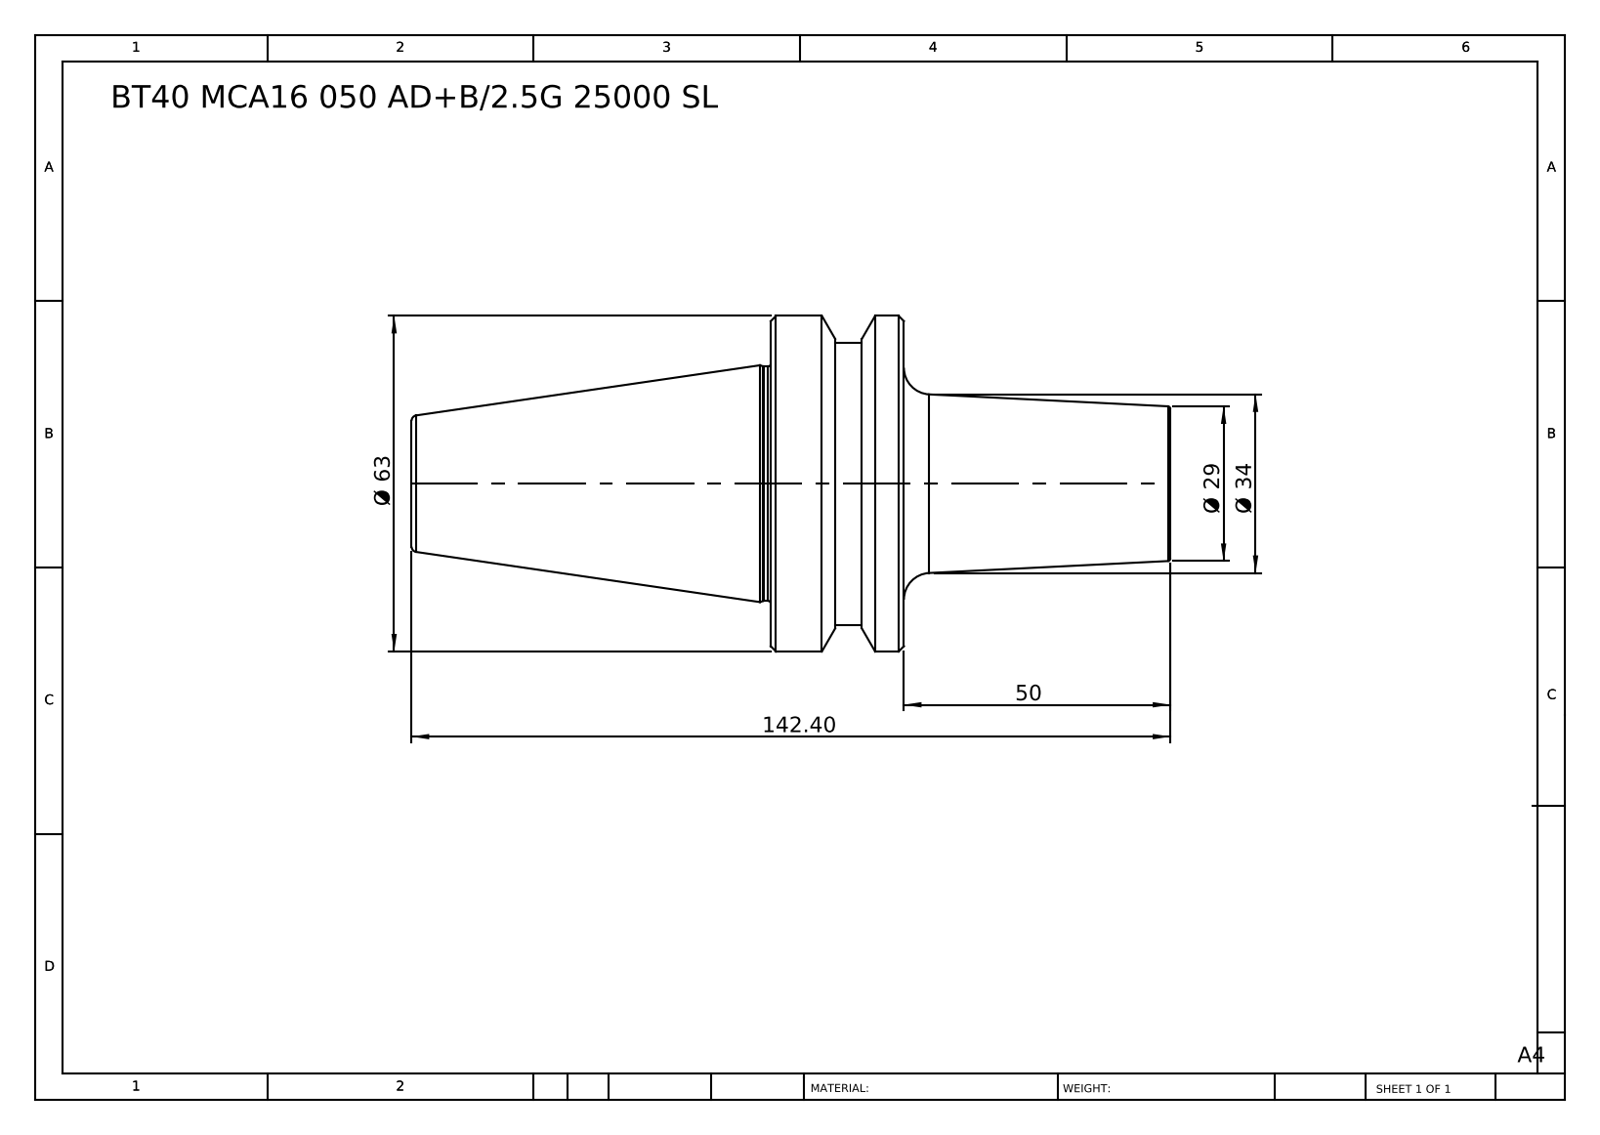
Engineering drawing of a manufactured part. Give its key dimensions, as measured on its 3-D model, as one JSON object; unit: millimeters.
{"part_name": "BT40 MCA16 050 AD+B-2.5G 25000 SL", "step_written_by": "SolidWorks 2014 (CONFIG_CONTROL_DESIGN)", "units": "millimeters", "bodies": {"solids": 1, "faces": 38, "planar": 6, "cylindrical": 8, "other": 24}, "overall_size": [142.4, 63, 63], "volume_mm3": 177929, "surface_area_mm2": 22829, "round_bosses_or_shafts": [[63, 1], [53, 1], [44, 1]], "face_to_face_distances": [25, 50, 75, 142.4, 92.4, 67.4, 62.9, 12.9, 12.1, 79.5]}
